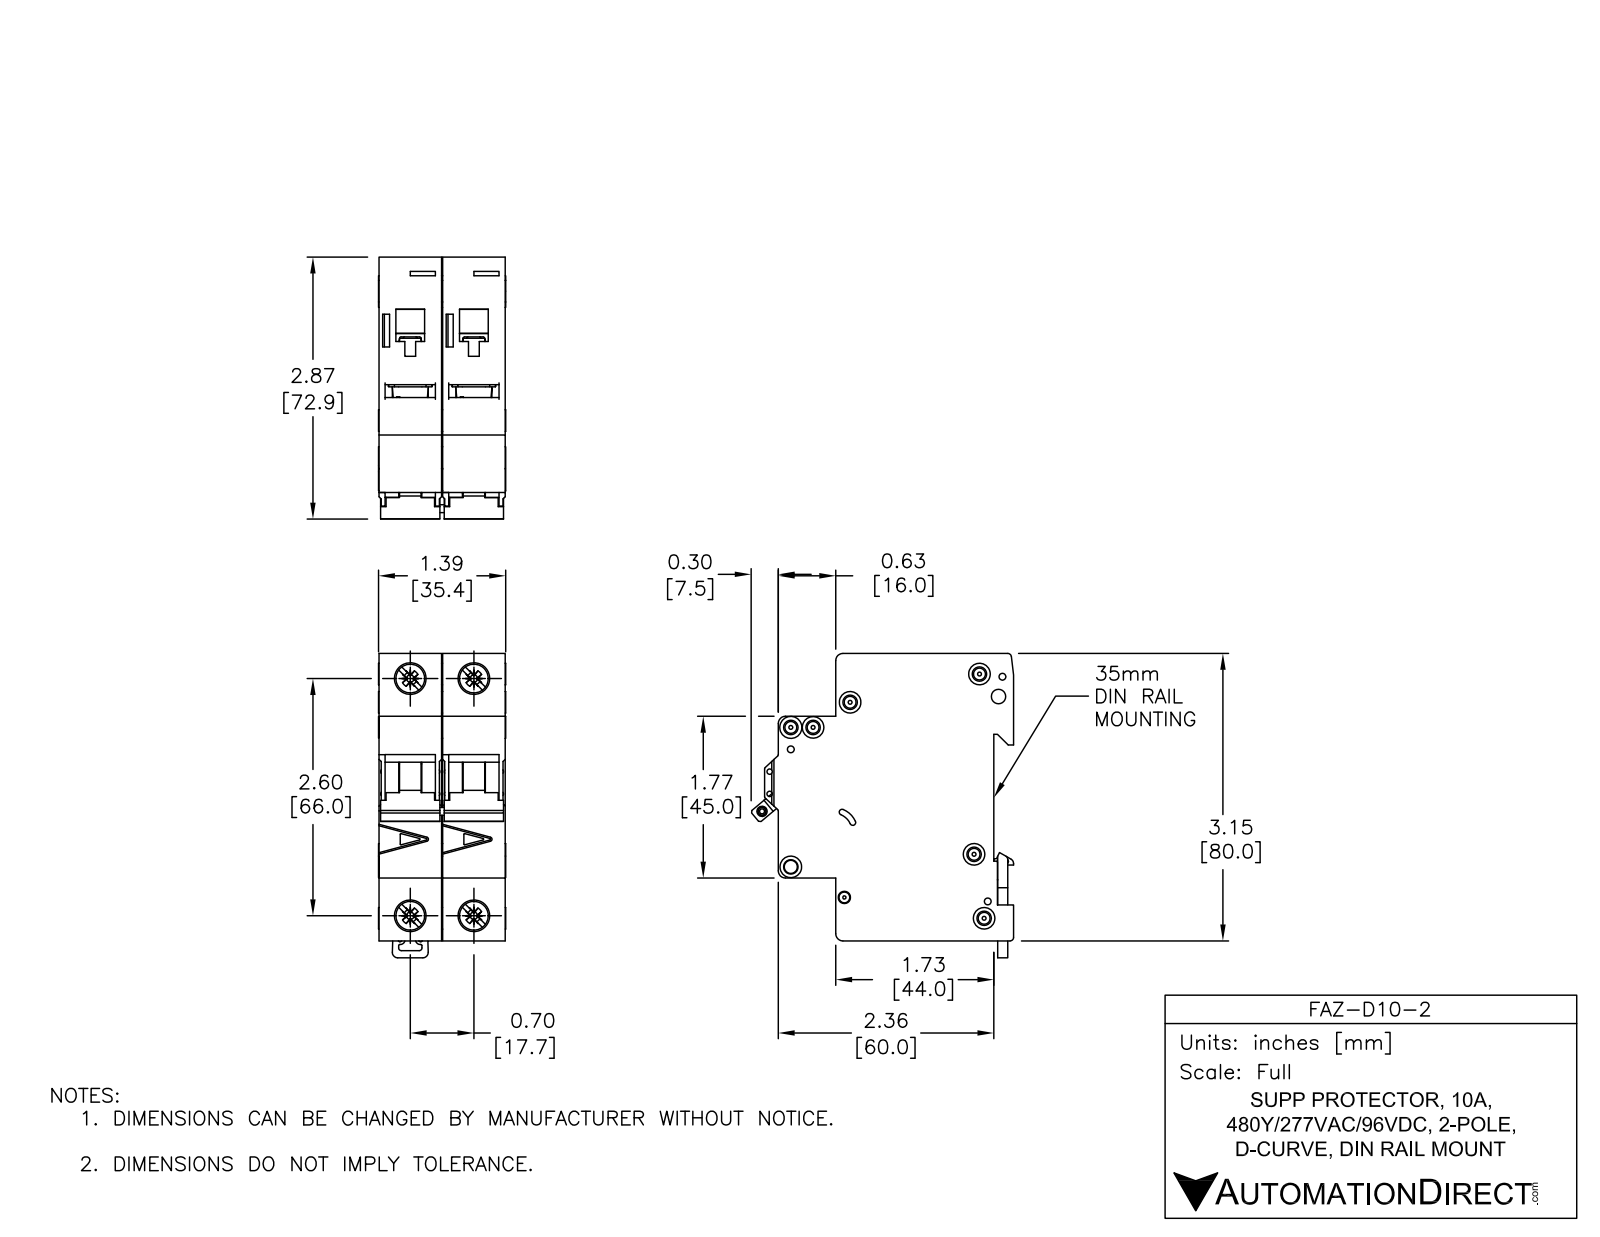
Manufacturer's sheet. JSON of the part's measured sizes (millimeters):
{"part_name": "FAZ-D10-2", "step_written_by": "SolidWorks 2014 (AUTOMOTIVE_DESIGN)", "units": "millimeters", "bodies": {"solids": 8, "faces": 1104, "planar": 466, "cylindrical": 396, "other": 242}, "overall_size": [84.78, 73.04, 35.4], "volume_mm3": 149808, "surface_area_mm2": 38799, "round_holes": [[3.6, 6], [1.9, 3], [1.09, 2], [1.5, 2], [4, 2], [7.15, 2], [8.2, 2], [2.15, 1], [2.2, 1], [2.55, 1], [3.3, 1], [3.4, 1]], "round_bosses_or_shafts": [[6, 4], [8.2, 2], [2.5, 2]], "partial_cylinders_radius": [[0.25, 49], [0.5, 19], [2, 10], [0.2, 8], [1, 8], [0.8, 2], [1.8, 2], [3, 2]], "face_to_face_distances": [17.7, 17.5, 35.2, 79.48, 5.5, 49.5, 44, 65.5, 60, 16], "hole_center_spacings": [6.2, 13.64, 17.7, 66, 68.33, 4.81, 5.19, 5.61]}
